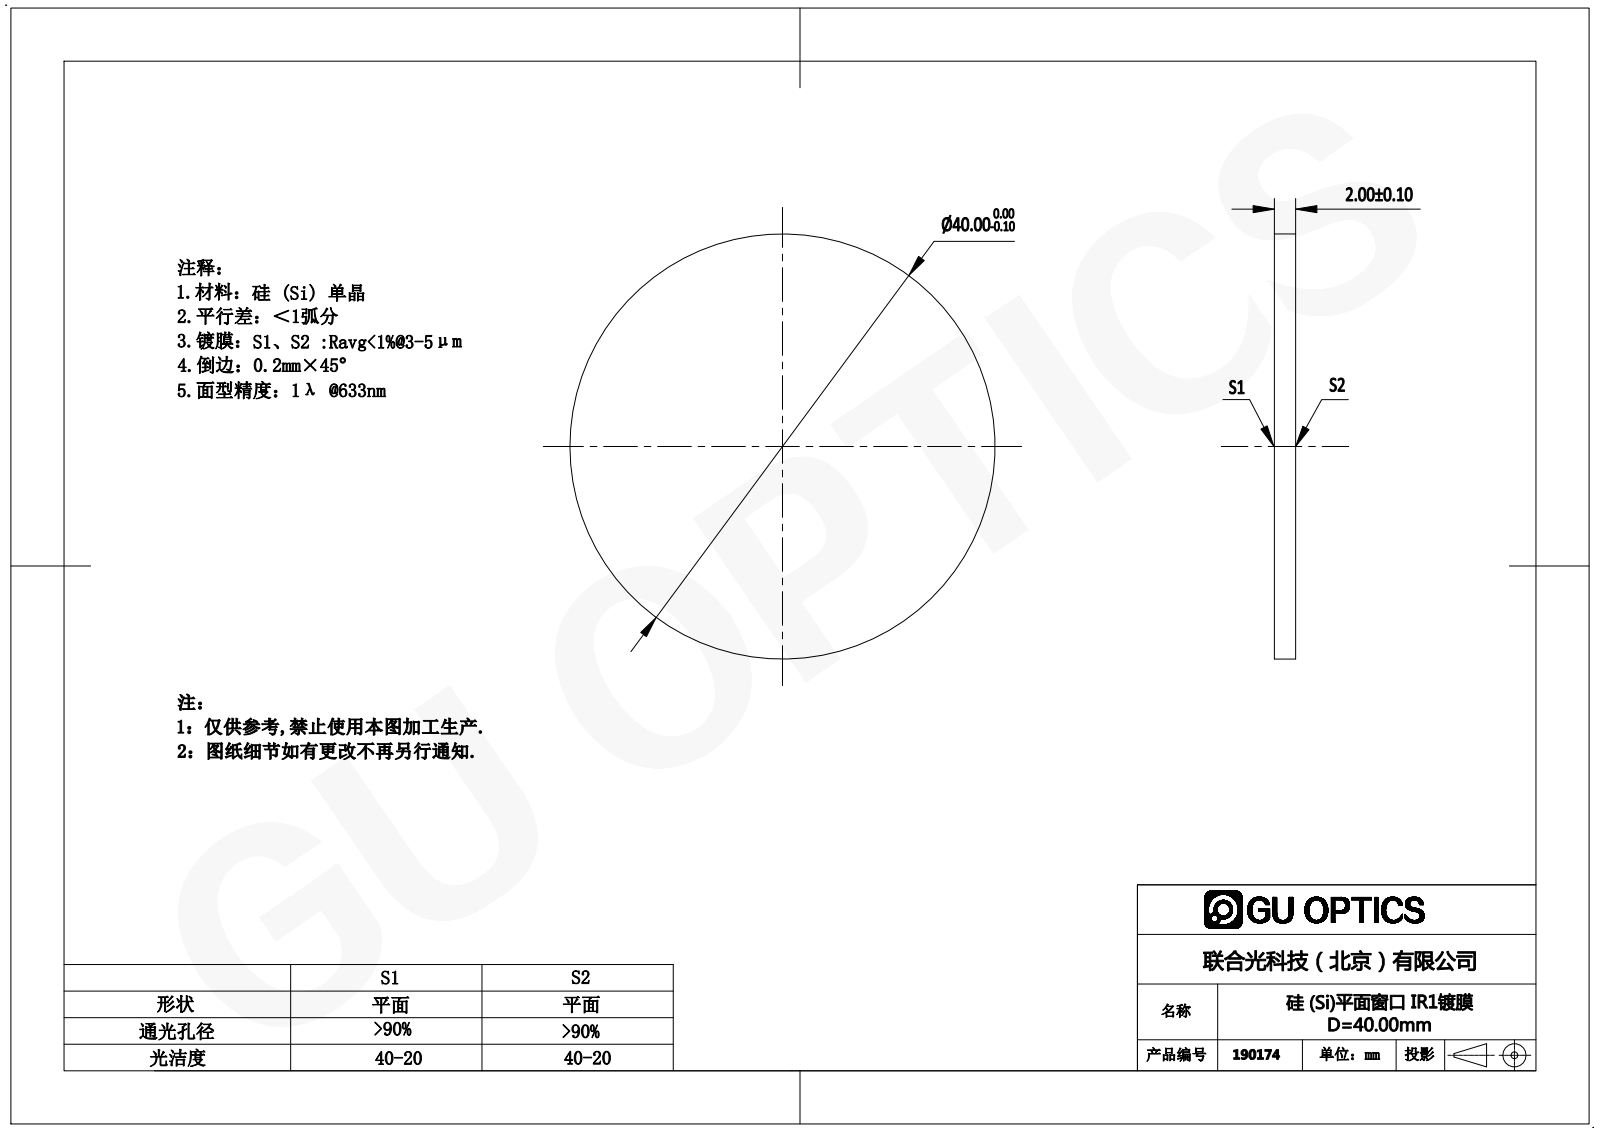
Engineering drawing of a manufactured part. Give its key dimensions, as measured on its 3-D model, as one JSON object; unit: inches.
{"part_name": "190167", "step_written_by": "SolidWorks 2016 (AUTOMOTIVE_DESIGN)", "units": "inches", "bodies": {"solids": 1, "faces": 4, "planar": 2, "cylindrical": 2, "other": 0}, "overall_size": [1.575, 1.575, 0.079], "volume_in3": 0.153, "surface_area_in2": 4.286, "round_bosses_or_shafts": [[1.575, 1]], "face_to_face_distances": [0.079]}
